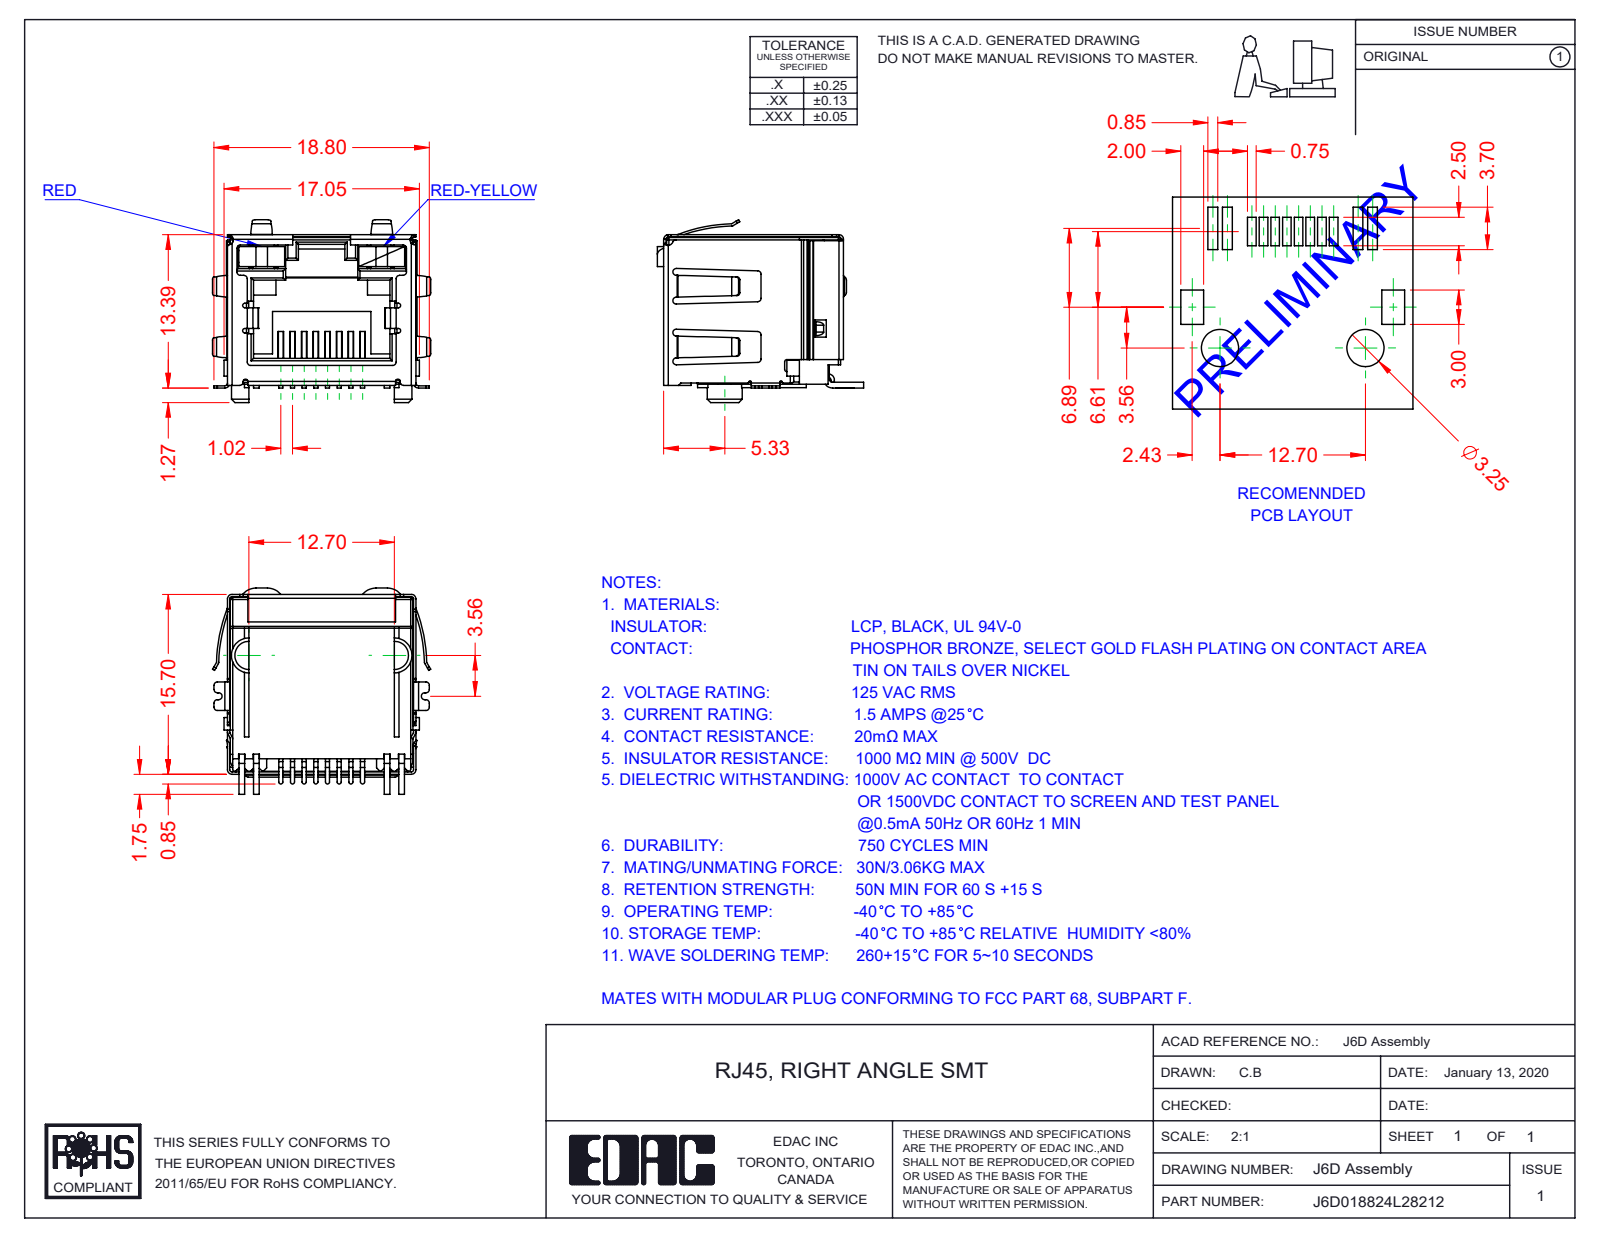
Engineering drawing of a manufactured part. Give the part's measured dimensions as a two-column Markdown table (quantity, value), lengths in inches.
| quantity | value |
| --- | --- |
| part name | J6D018824L28212; 6D Insulator; 6D Shield_LED - EMI; 6D LED RH_8-Red-Yellow (+2 more) |
| STEP written by | SolidWorks 2016 (CONFIG_CONTROL_DESIGN) |
| units | inches |
| bodies | 12 solids, 1031 faces (702 planar, 284 cylindrical, 45 other) |
| overall size | 0.75 × 0.709 × 0.628 |
| volume | 0.109 in³ |
| surface area | 7.434 in² |
| partial cylindrical surfaces (radius × count) | 0.012 × 55, 0.008 × 40, 0.016 × 19, 0.01 × 16, 0.004 × 12, 0.006 × 8, 0.007 × 8, 0.02 × 6 |
| main face-to-face distances | 0.63, 0.638, 0.64, 0.089, 0.039, 0.628, 0.504, 0.018, 0.514, 0.417 |
